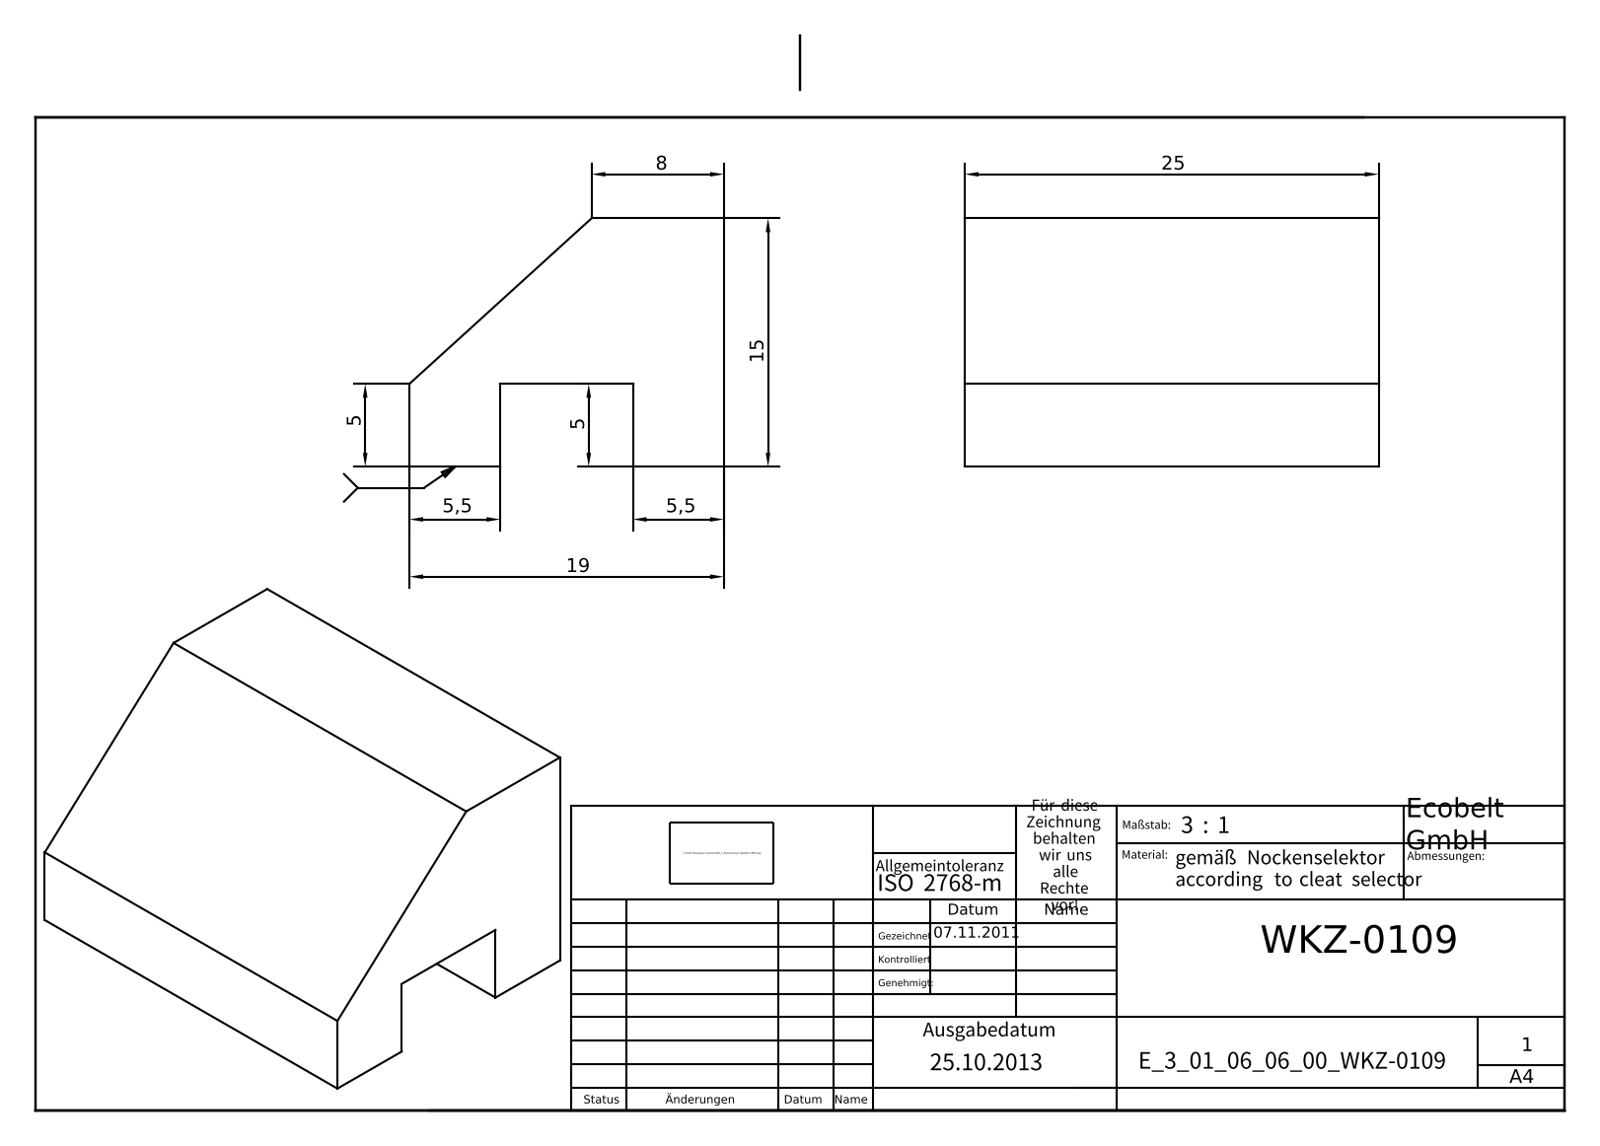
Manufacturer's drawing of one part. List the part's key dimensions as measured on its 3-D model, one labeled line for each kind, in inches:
Part name (STEP PRODUCT): E_3_01_06_06_00_WKZ-0109
STEP written by: Autodesk Inventor 2025 (AUTOMOTIVE_DESIGN)
Units: inches
Bodies: 1 solid, 11 faces (11 planar, 0 cylindrical, 0 other)
Overall size (bounding box): 0.984 × 0.748 × 0.591
Volume: 0.29 in³ · Surface area: 3.374 in²
Main face-to-face distances: 0.217, 0.531, 0.197, 0.591, 0.394, 0.984, 0.748, 0.315
